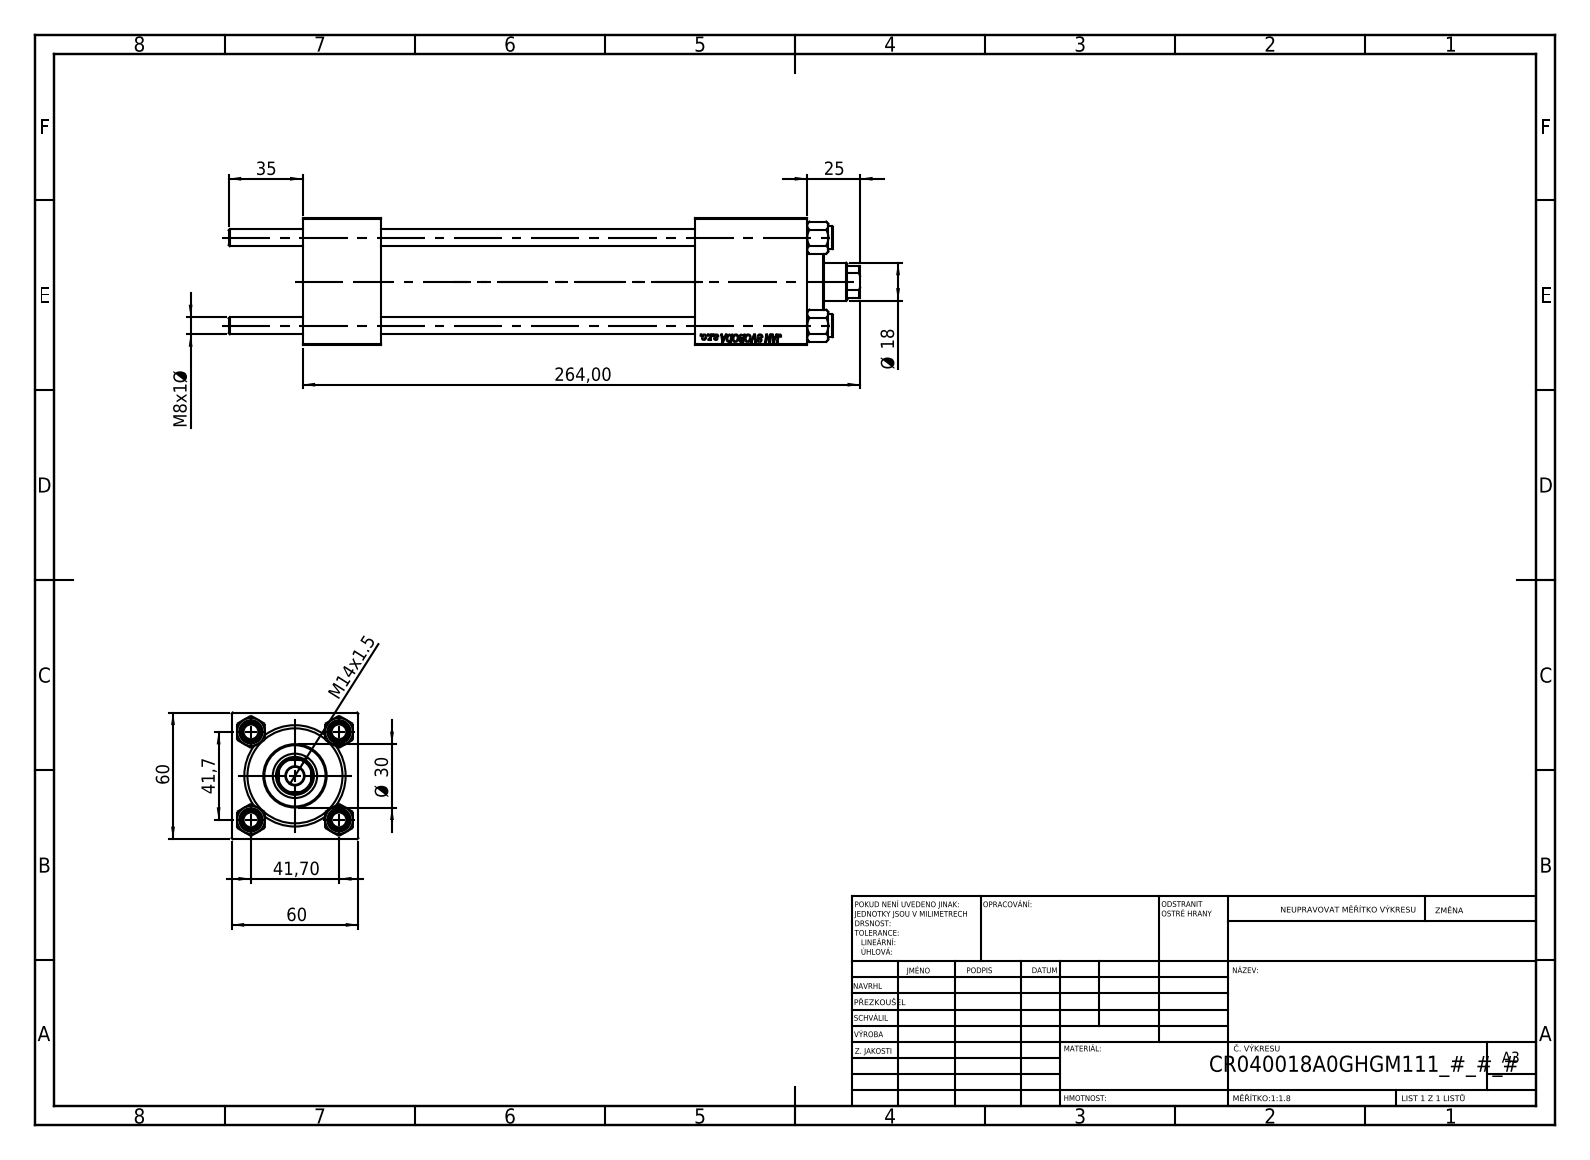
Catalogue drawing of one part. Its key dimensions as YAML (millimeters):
part_name: "CR025_012_A_0_G_A_G_M_020_+#_##_TYCINKA; V215_VC_A; V215CR_BODY_A; V215CR_VCP (+1 more)"
step_written_by: "SolidWorks 2019 (CONFIG_CONTROL_DESIGN)"
units: millimeters
bodies: {solids: 11, faces: 1135, planar: 521, cylindrical: 78, other: 536}
overall_size: [299, 60, 60]
volume: 492232
surface_area: 152886
round_holes:
  - {diameter: 8, count: 4}
  - {diameter: 7, count: 2}
  - {diameter: 16.66, count: 2}
  - {diameter: 24, count: 2}
  - {diameter: 8.5, count: 1}
  - {diameter: 18, count: 1}
  - {diameter: 21, count: 1}
  - {diameter: 31, count: 1}
  - {diameter: 40, count: 1}
  - {diameter: 45, count: 1}
round_bosses_or_shafts:
  - {diameter: 11, count: 4}
  - {diameter: 46, count: 1}
  - {diameter: 30, count: 1}
partial_cylinders:
  - {radius: 8.5, count: 1}
face_to_face_distances: [60, 37, 239, 202, 53, 186, 149, 210.3, 173.3, 24.3]
hole_center_spacings: [29.49, 41.7, 58.97, 183.5]
